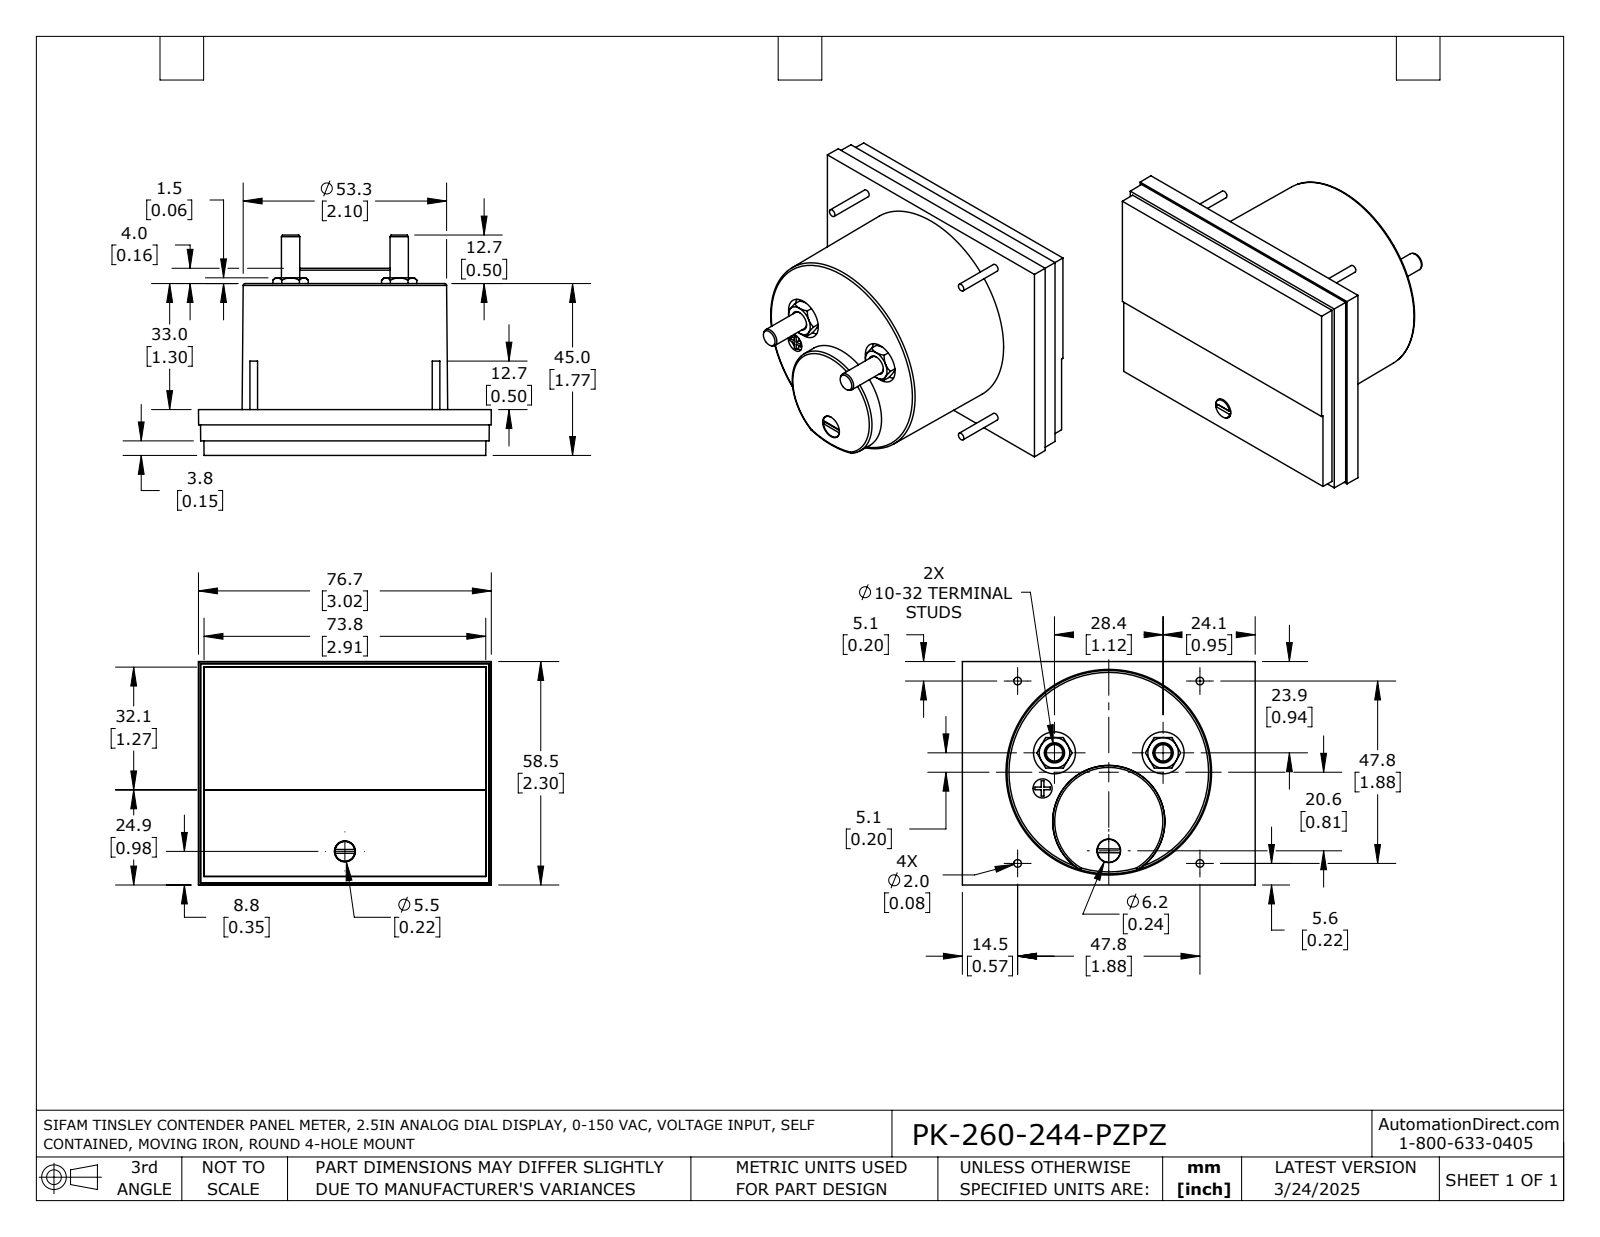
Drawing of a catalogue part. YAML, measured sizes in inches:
part_name: "PK-260-244-PZPZ"
step_written_by: "SolidWorks 2021 (AUTOMOTIVE_DESIGN)"
units: inches
bodies: {solids: 1, faces: 192, planar: 95, cylindrical: 37, other: 60}
overall_size: [3.02, 2.303, 2.272]
volume: 7.657
surface_area: 36.55
round_holes:
  - {diameter: 0.197, count: 3}
  - {diameter: 0.433, count: 2}
  - {diameter: 0.209, count: 1}
  - {diameter: 0.217, count: 1}
  - {diameter: 0.244, count: 1}
round_bosses_or_shafts:
  - {diameter: 0.079, count: 4}
  - {diameter: 0.189, count: 2}
  - {diameter: 0.236, count: 1}
  - {diameter: 0.205, count: 1}
partial_cylinders:
  - {radius: 0.033, count: 1}
face_to_face_distances: [0.02, 0.472, 0.13, 0.322, 0.15, 0.453, 0.057, 0.077, 0.396, 0.073]
hole_center_spacings: [1.155, 1.16, 0.387, 0.938, 0.942, 1.12, 1.295]
